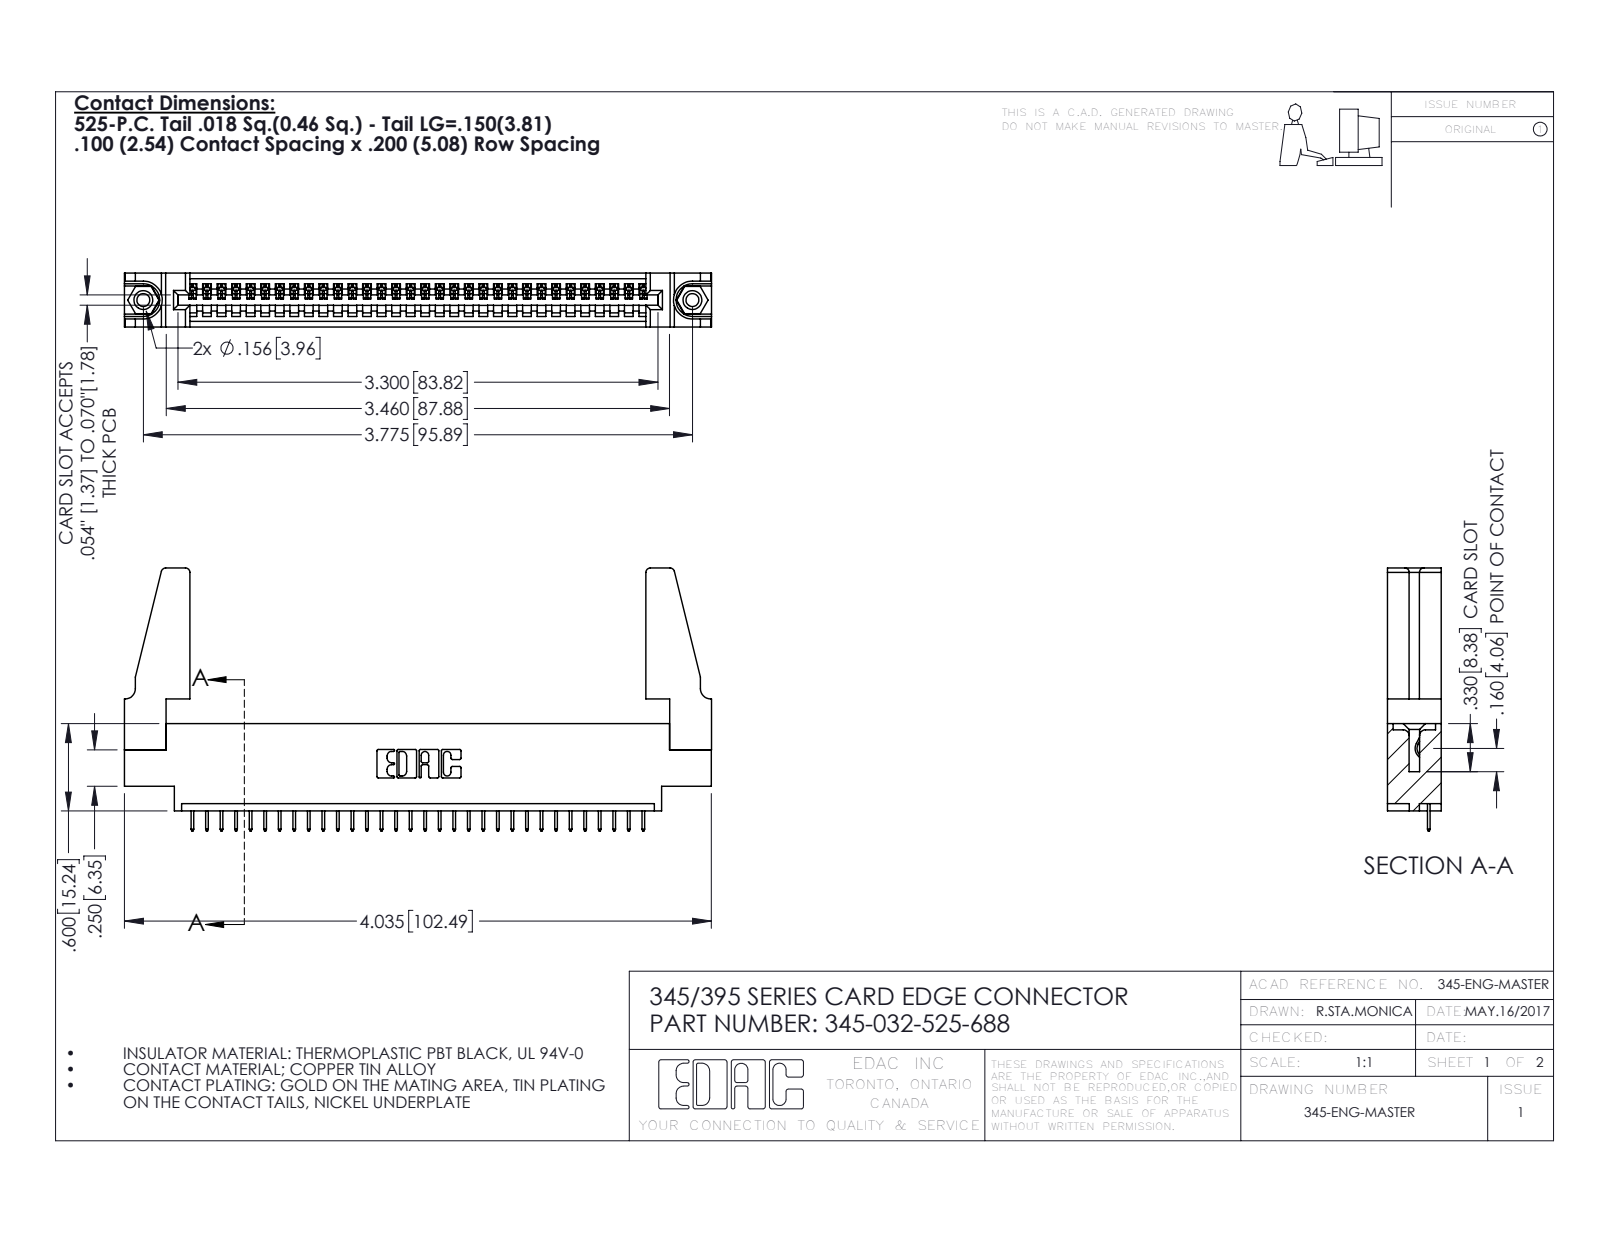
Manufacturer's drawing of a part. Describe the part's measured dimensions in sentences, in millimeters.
The part is named "345-292-001_345-293-125; 345-250-001_345-250-001-102; 345 Part_0.170 Offset - 0.156 Dia-TH; 345-032-525-688 (+1 more)". Its 3-D file was written by "SolidWorks 2020 (CONFIG_CONTROL_DESIGN)". It is 37 solids with 2238 faces: 1628 planar, 594 cylindrical and 16 other. Overall it measures 102.5 by 45.9 by 9.4 millimeters. Its volume is 12 700 cubic millimeters and its surface area 15 190 square millimeters. Round holes: 2 of diameter 2.3, 2 of diameter 3.2, 2 of diameter 4, 1 of diameter 1.6. Round bosses or shafts: 2 of diameter 3.9. Partial cylindrical surfaces (rounded edges, fillets, slot ends): 64 of radius 0.2, 22 of radius 0.3, 8 of radius 0.8, 6 of radius 0.2, 6 of radius 0.8, 3 of radius 0.7, 2 of radius 0.8, 2 of radius 1. The main face-to-face distances are 9.4, 1.8, 7.6, 5.1, 2.5, 6.9, 0.6, 5.7, 4.4, 1.8. The hole center spacings are 6.9, 89.9, 95.9.
